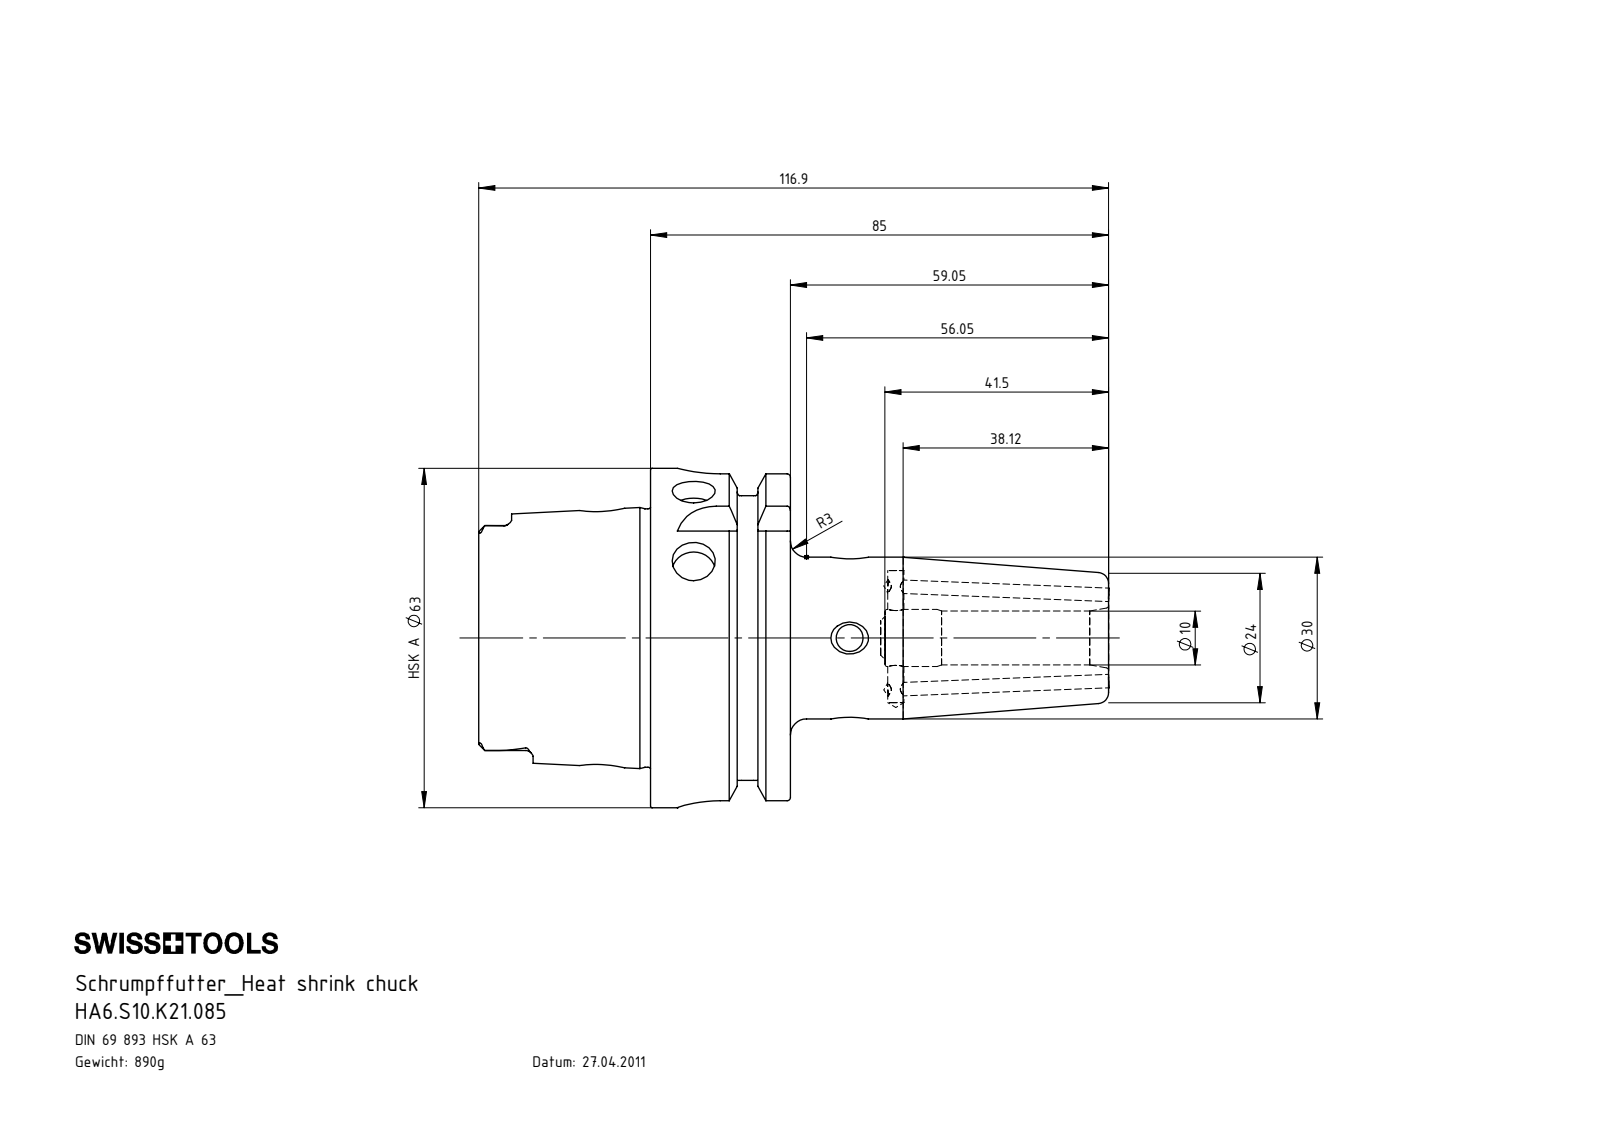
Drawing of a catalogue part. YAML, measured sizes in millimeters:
part_name: "ERU-AN3.K01.020_A; HA6-S10.K21.085_C_Fertigbearbeitung; HA6.S10.K21.085; ERU-CJ2.001.006_Default"
step_written_by: "SolidWorks 2011 (CONFIG_CONTROL_DESIGN)"
units: millimeters
bodies: {solids: 4, faces: 307, planar: 101, cylindrical: 85, other: 121}
overall_size: [116.98, 63, 63]
volume: 113338
surface_area: 31111
round_holes:
  - {diameter: 2.5, count: 2}
  - {diameter: 5, count: 2}
  - {diameter: 8, count: 2}
  - {diameter: 10, count: 2}
  - {diameter: 3, count: 1}
  - {diameter: 4, count: 1}
  - {diameter: 6.4, count: 1}
  - {diameter: 7.5, count: 1}
  - {diameter: 10.6, count: 1}
  - {diameter: 17, count: 1}
  - {diameter: 19, count: 1}
  - {diameter: 34, count: 1}
round_bosses_or_shafts:
  - {diameter: 3, count: 2}
  - {diameter: 63, count: 1}
  - {diameter: 54.95, count: 1}
  - {diameter: 47.94, count: 1}
  - {diameter: 30, count: 1}
  - {diameter: 8, count: 1}
  - {diameter: 7, count: 1}
partial_cylinders:
  - {radius: 1.4, count: 6}
  - {radius: 2.88, count: 4}
  - {radius: 8, count: 4}
face_to_face_distances: [25.95, 16, 9.95, 31.9, 41.85, 57.85, 52.8, 21.8, 11.85, 53.7]
hole_center_spacings: [8.55, 29.95, 45.95, 54.5]
